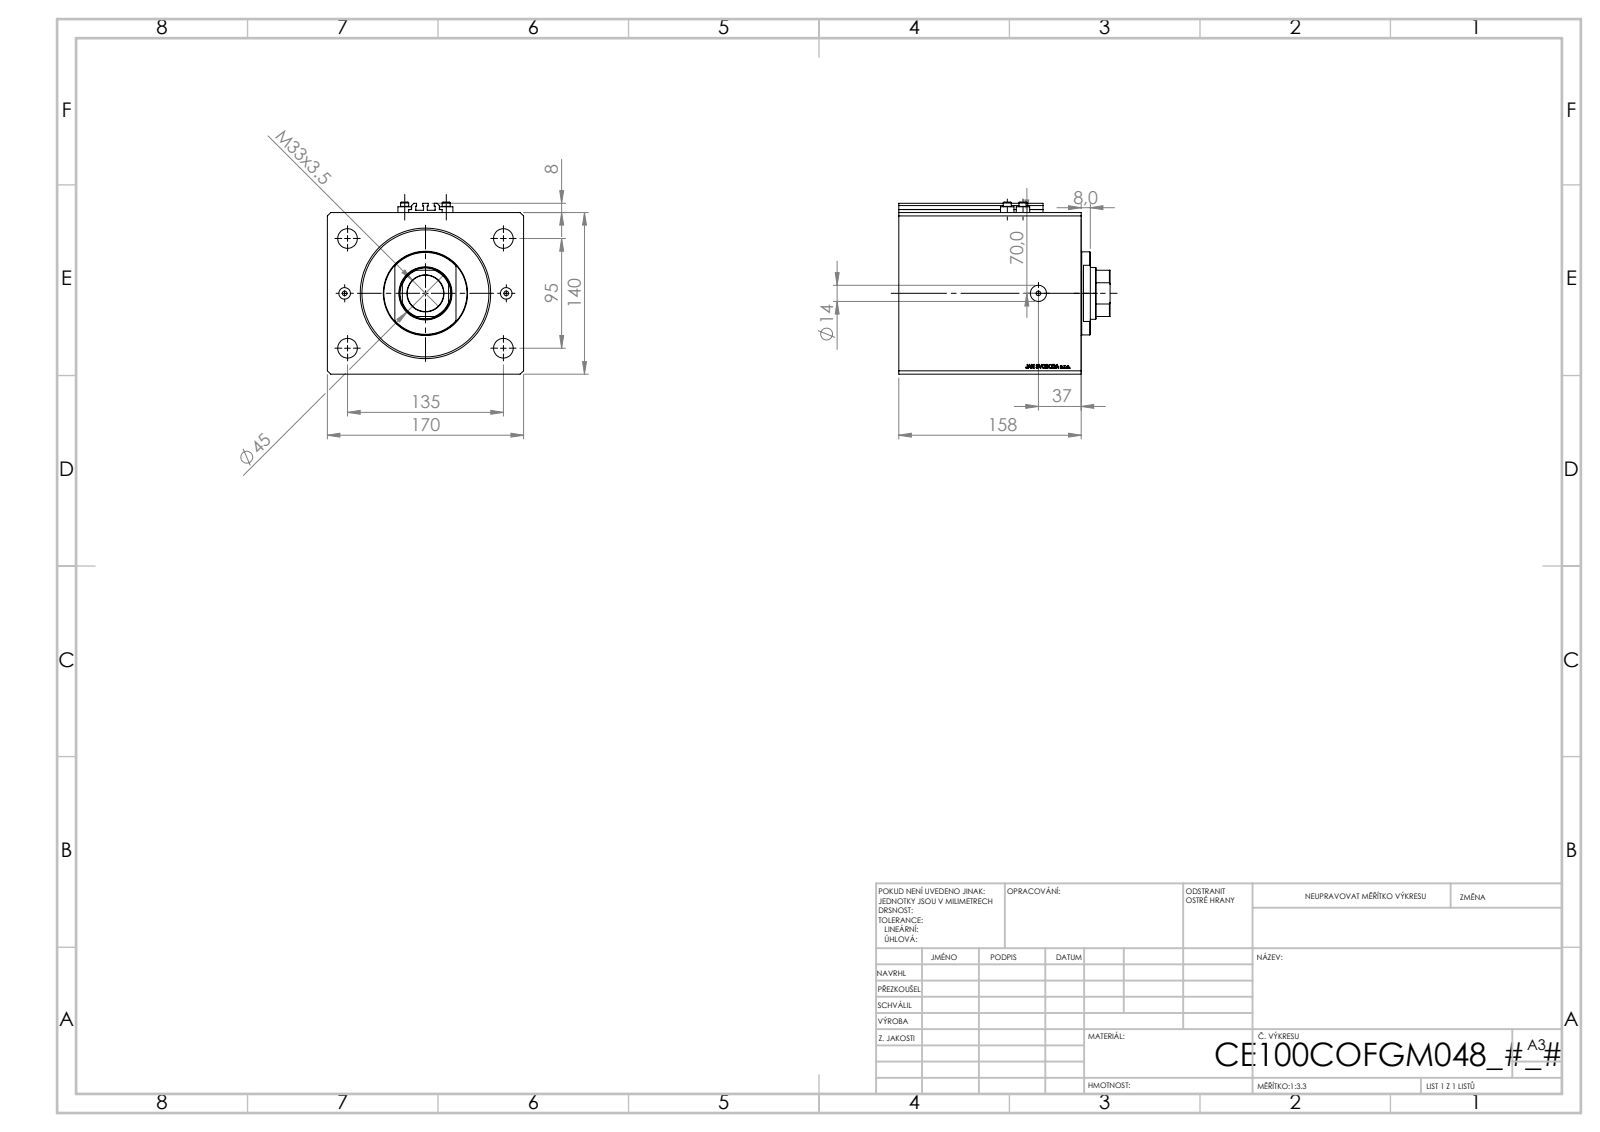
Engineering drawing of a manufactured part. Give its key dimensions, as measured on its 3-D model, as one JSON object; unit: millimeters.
{"part_name": "V250CE_VC_C; ALLEN BOLT V250CE; V250CE_C_VCP; V250CE_C_Body", "step_written_by": "SolidWorks 2019 (CONFIG_CONTROL_DESIGN)", "units": "millimeters", "bodies": {"solids": 8, "faces": 1034, "planar": 504, "cylindrical": 86, "other": 444}, "overall_size": [183, 170, 149], "volume_mm3": 3337000, "surface_area_mm2": 319805, "round_holes": [[4, 8], [17, 4], [10, 2], [14, 2], [31.5, 1], [45, 1], [100, 1], [113, 1]], "round_bosses_or_shafts": [[11.6, 4], [7, 4], [72, 1]], "partial_cylinders_radius": [[0.2, 10], [22, 1]], "face_to_face_distances": [140, 170, 158, 28.9, 129.1, 25, 133, 104.1, 73, 85], "hole_center_spacings": [47.57, 82.54, 145.47, 13.6, 36, 38.48, 70, 95]}
